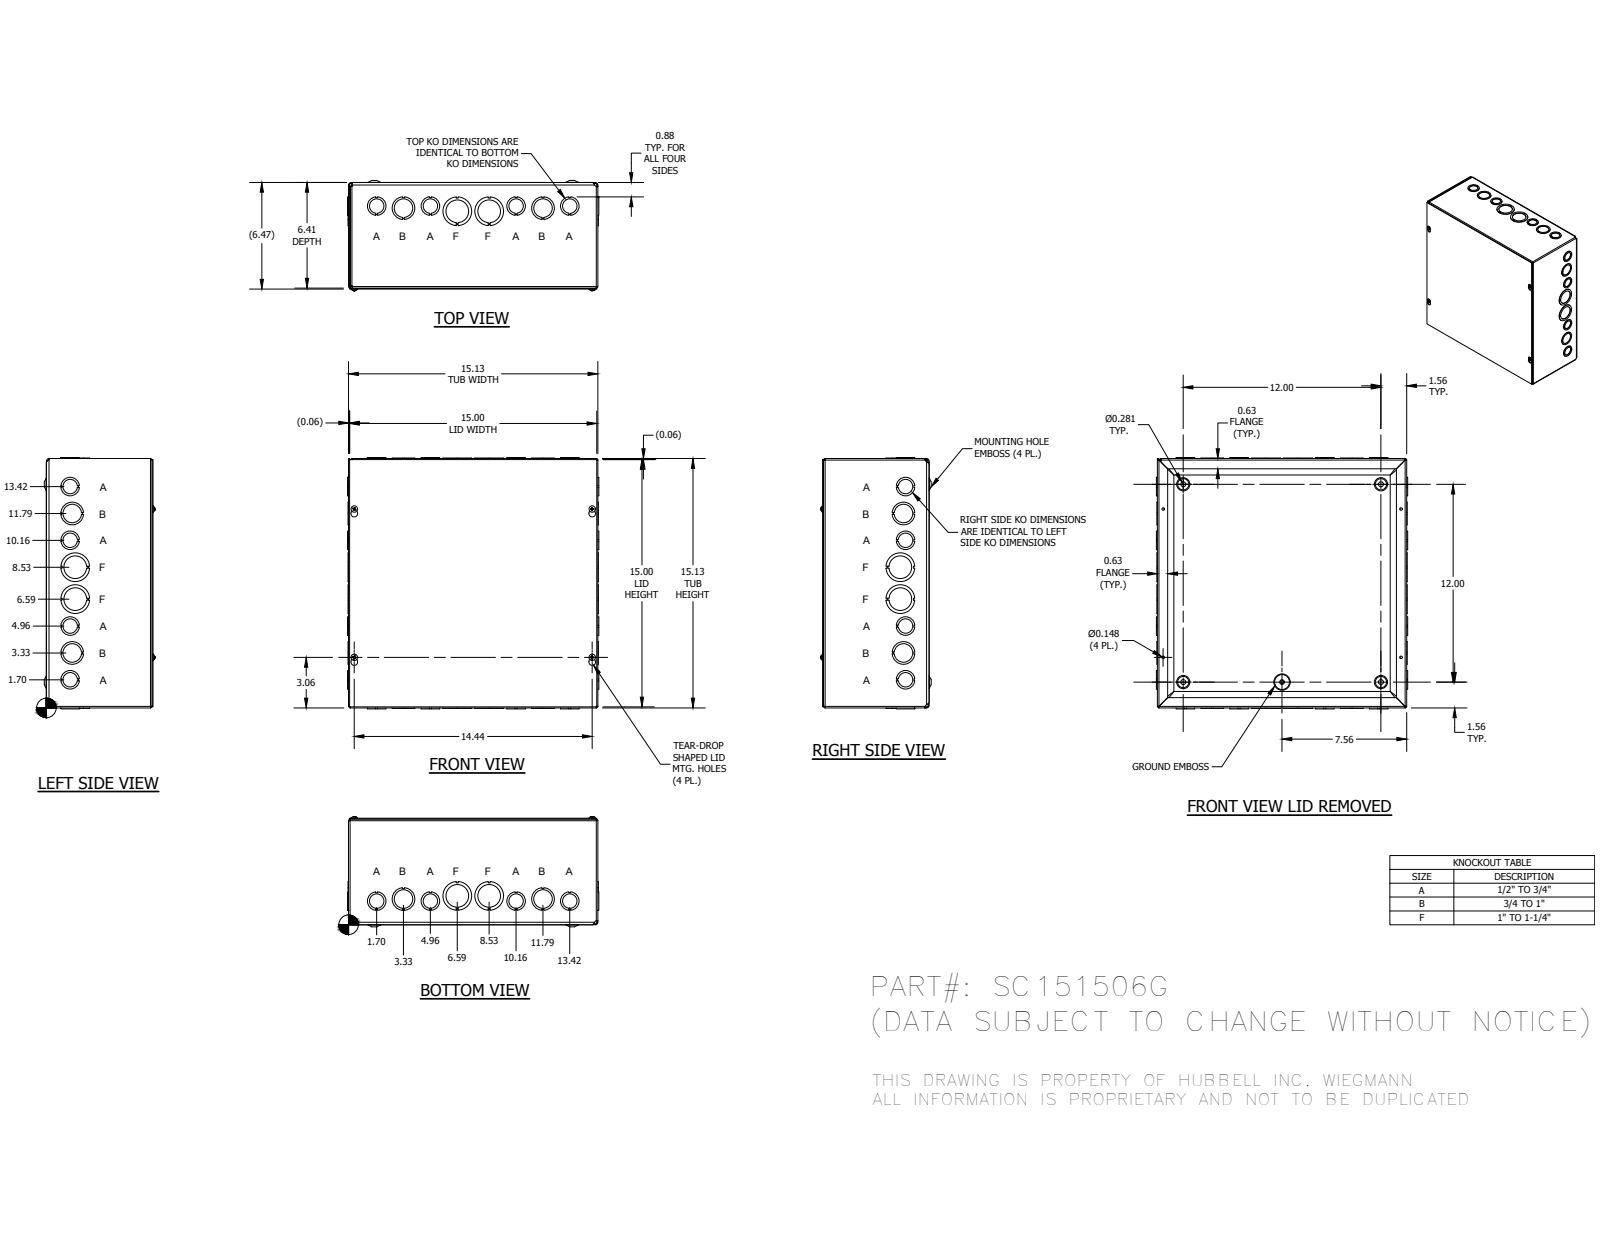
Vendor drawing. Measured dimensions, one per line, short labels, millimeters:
name: SC1515GBKP; SC151506GWRA; SC1515GLID; 34056 (+1 more)
written by: Autodesk Inventor 2014 (AUTOMOTIVE_DESIGN)
unit: mm
bodies: 38 solids, 1254 faces (838 planar, 265 cylindrical, 151 other)
size: 387.32 × 387.32 × 170
holes: 12× ⌀28.57, 8× ⌀22.22, 8× ⌀34.92, 4× ⌀3.76, 4× ⌀7.62, 4× ⌀44.45, 1× ⌀4.19
bosses: 4× ⌀9.75, 4× ⌀4.17, 1× ⌀5.8
rounds: 8× R0.79, 8× R2.37, 4× R1.4, 4× R1.57, 4× R2.38, 4× R2.79, 4× R2.97, 4× R3.15
face distances: 1.57, 161.12, 162.69, 1.59, 1.58, 162.71, 164.28, 384.18, 382.6, 382.61
hole spacings: 41.52, 42.15, 49.09, 82.94, 91.03, 132.17, 173.51, 214.88
